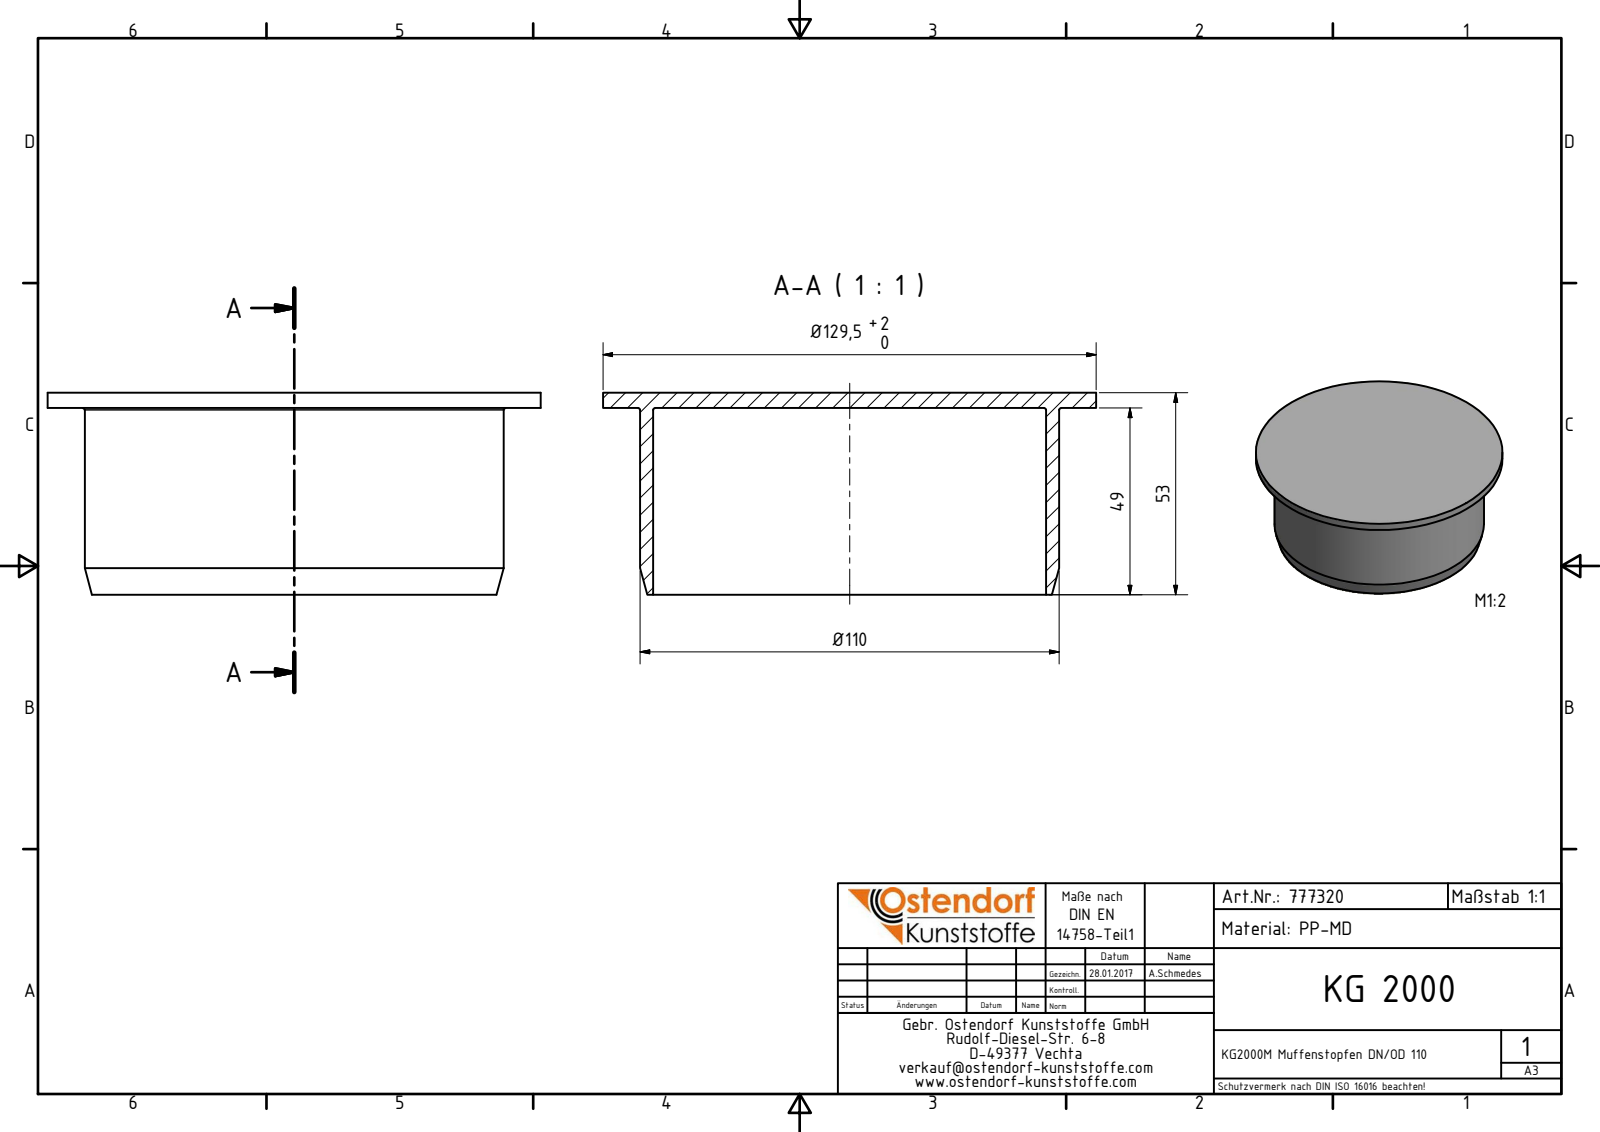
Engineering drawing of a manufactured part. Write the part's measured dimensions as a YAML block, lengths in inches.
part_name: "777320 KG2000M Muffenstopfen DN_OD 110"
step_written_by: "Autodesk Inventor 2016 (AUTOMOTIVE_DESIGN)"
units: inches
bodies: {solids: 1, faces: 10, planar: 4, cylindrical: 3, other: 3}
overall_size: [5.098, 5.098, 2.087]
volume: 6.485
surface_area: 93.08
round_holes:
  - {diameter: 4.063, count: 1}
round_bosses_or_shafts:
  - {diameter: 5.098, count: 1}
  - {diameter: 4.331, count: 1}
face_to_face_distances: [0.157, 1.929, 2.087]
